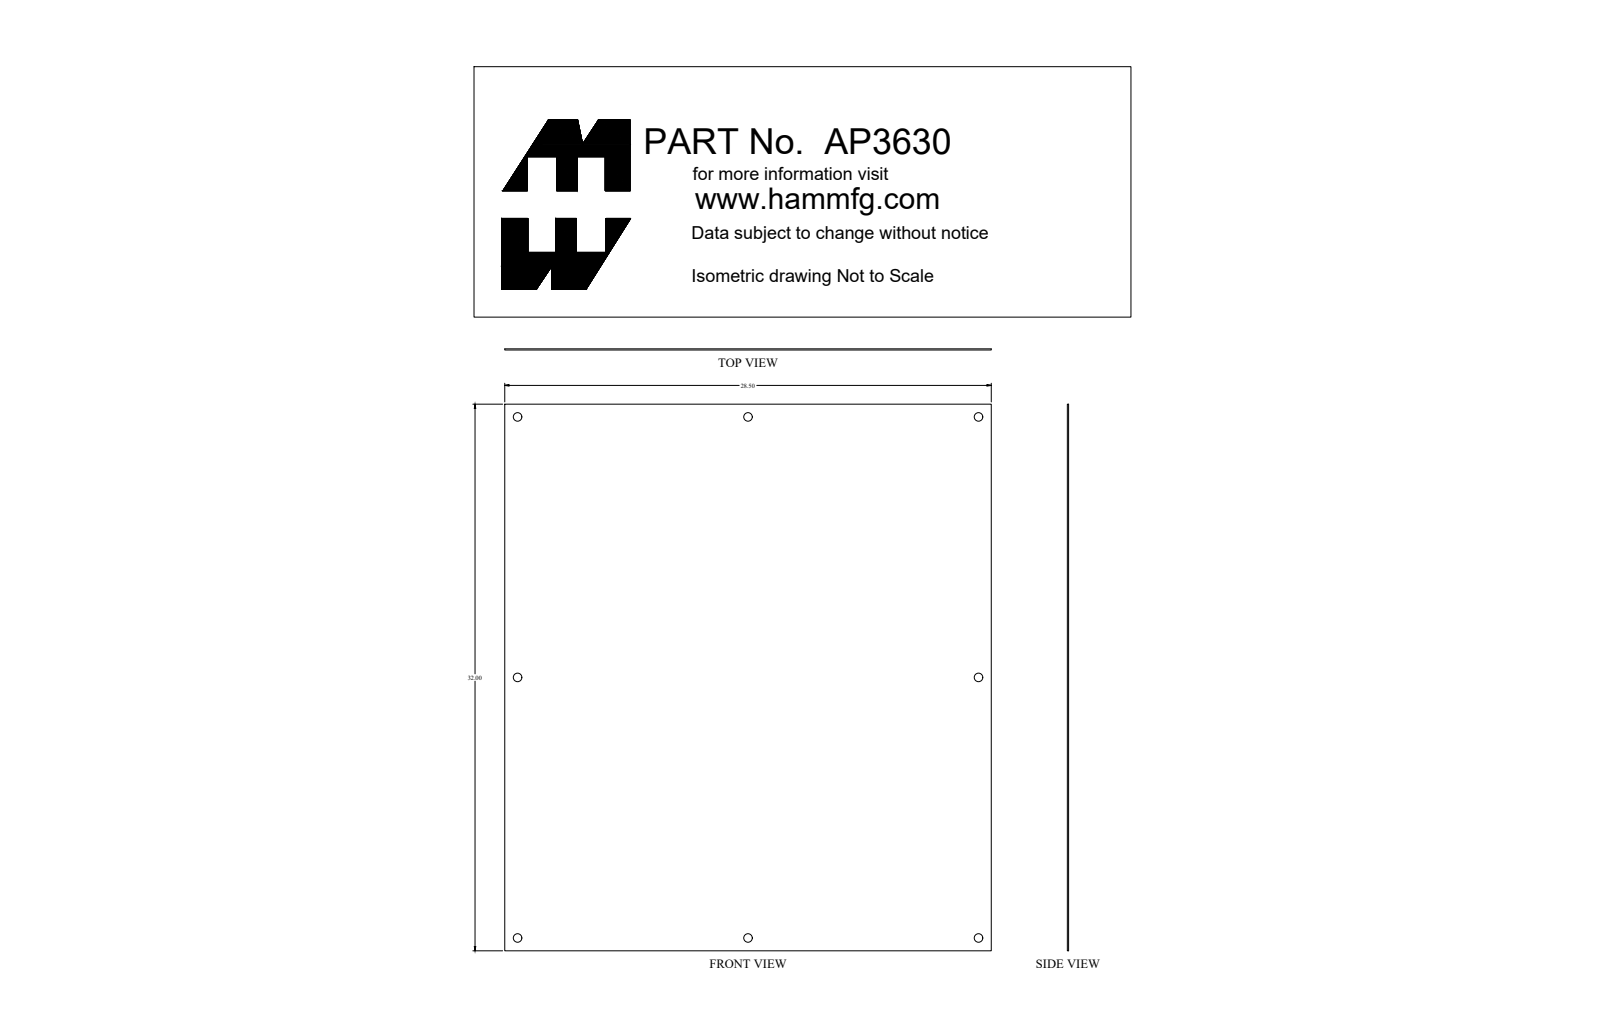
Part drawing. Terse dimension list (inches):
name: AP3630_Default
written by: SolidWorks 2019 (CONFIG_CONTROL_DESIGN)
unit: in
bodies: 1 solid, 22 faces (6 planar, 16 cylindrical, 0 other)
size: 32 × 28.5 × 0.072
volume: 65.55 in³; area: 1 830 in²
holes: 8× ⌀0.5
face distances: 0.072, 28.5, 32
hole spacings: 13.5, 15.25, 20.367, 31.009, 33.354, 27, 30.5, 40.734
